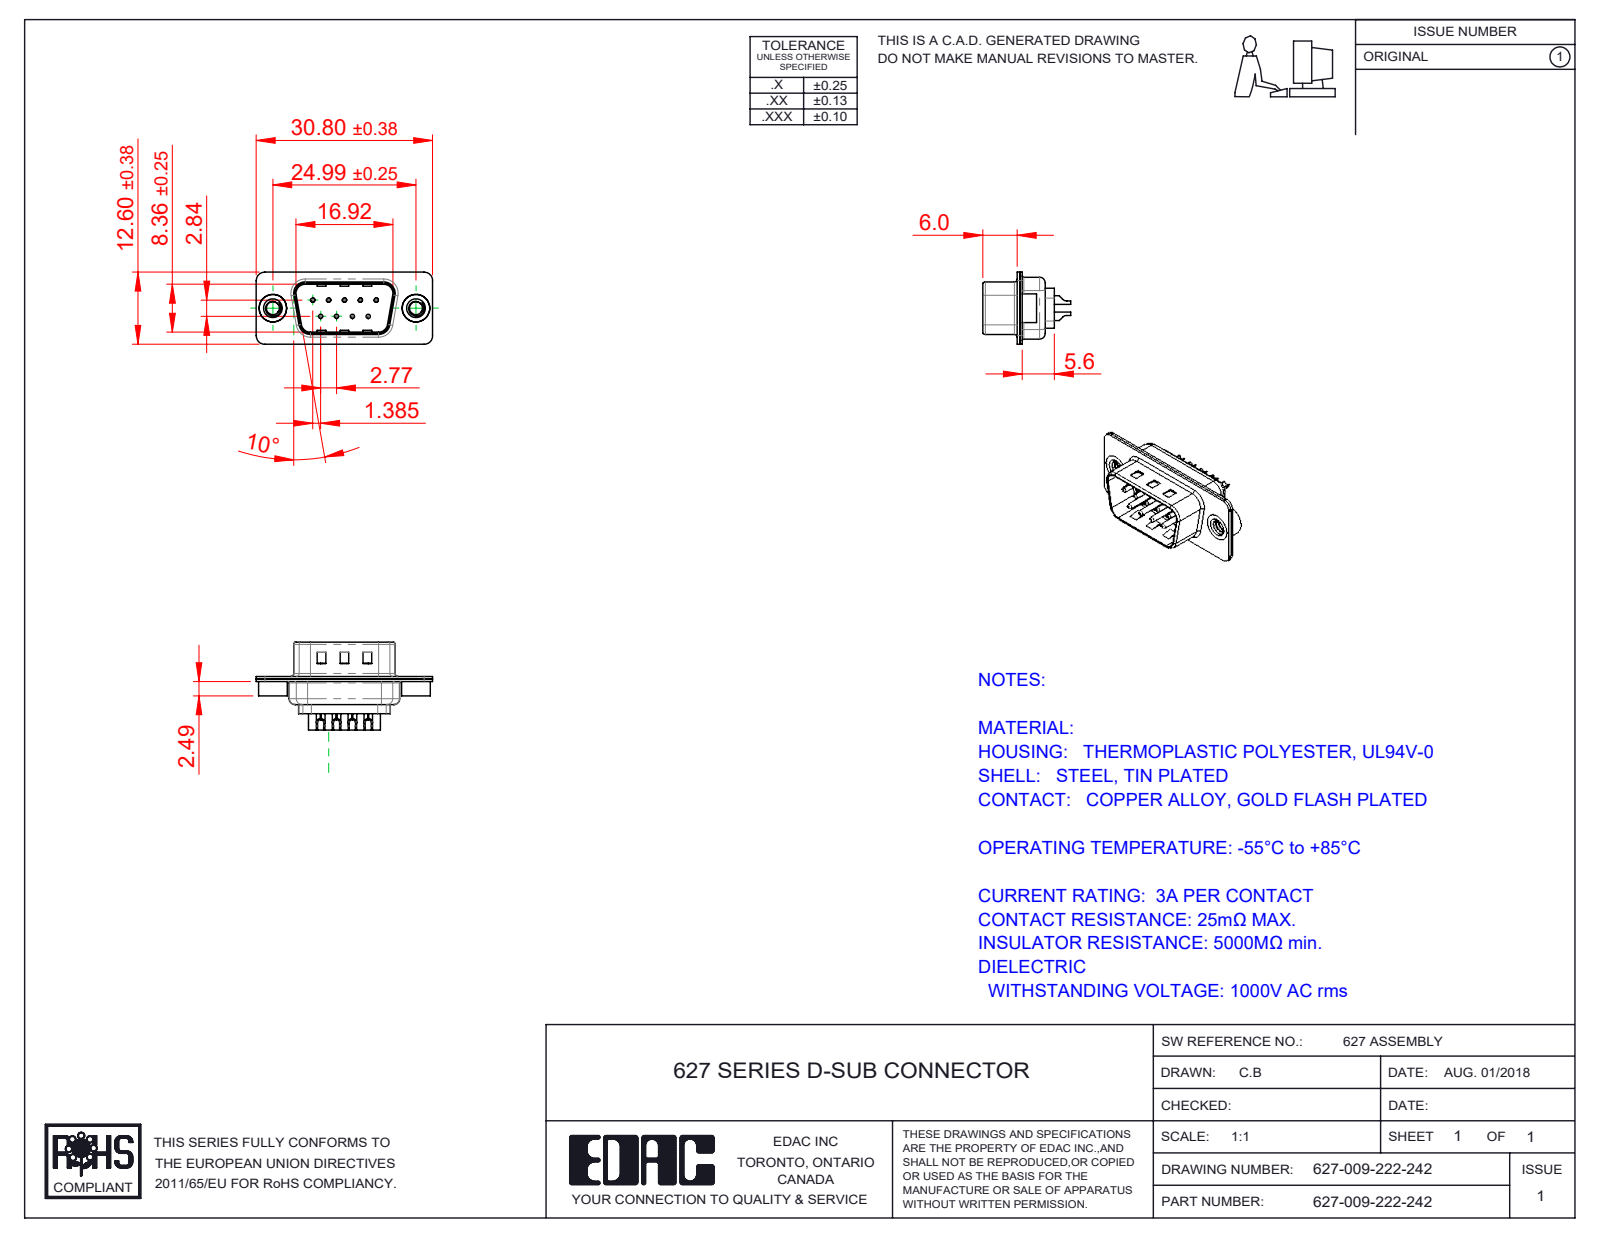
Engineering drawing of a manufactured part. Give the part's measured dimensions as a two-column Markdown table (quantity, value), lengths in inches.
| quantity | value |
| --- | --- |
| part name | 627 Contact Row 1_22L; 627 Shell Front_09 Contacts; 627 Housing_09 LP; 627-009-222-242 (+3 more) |
| STEP written by | SolidWorks 2020 (CONFIG_CONTROL_DESIGN) |
| units | inches |
| bodies | 14 solids, 876 faces (233 planar, 388 cylindrical, 255 other) |
| overall size | 1.213 × 0.604 × 0.496 |
| volume | 0.08 in³ |
| surface area | 6.11 in² |
| round holes (diameter × count) | 0.014 × 9, 0.043 × 9, 0.063 × 9, 0.089 × 2, 0.157 × 2, 0.189 × 2 |
| round bosses / shafts (diameter × count) | 0.079 × 9, 0.059 × 9, 0.03 × 9, 0.197 × 2, 0.193 × 2 |
| partial cylindrical surfaces (radius × count) | 0.059 × 18, 0.079 × 12, 0.02 × 8, 0.063 × 8, 0.039 × 6, 0.01 × 4, 0.024 × 4, 0.026 × 4 |
| main face-to-face distances | 0.018, 0.016, 0.035, 0.032, 0.377, 0.055, 0.345, 0.02, 0.059, 0.256 |
| hole center spacings | 0.124, 0.109, 0.218, 0.198, 0.198, 0.327, 0.294, 0.295 |
